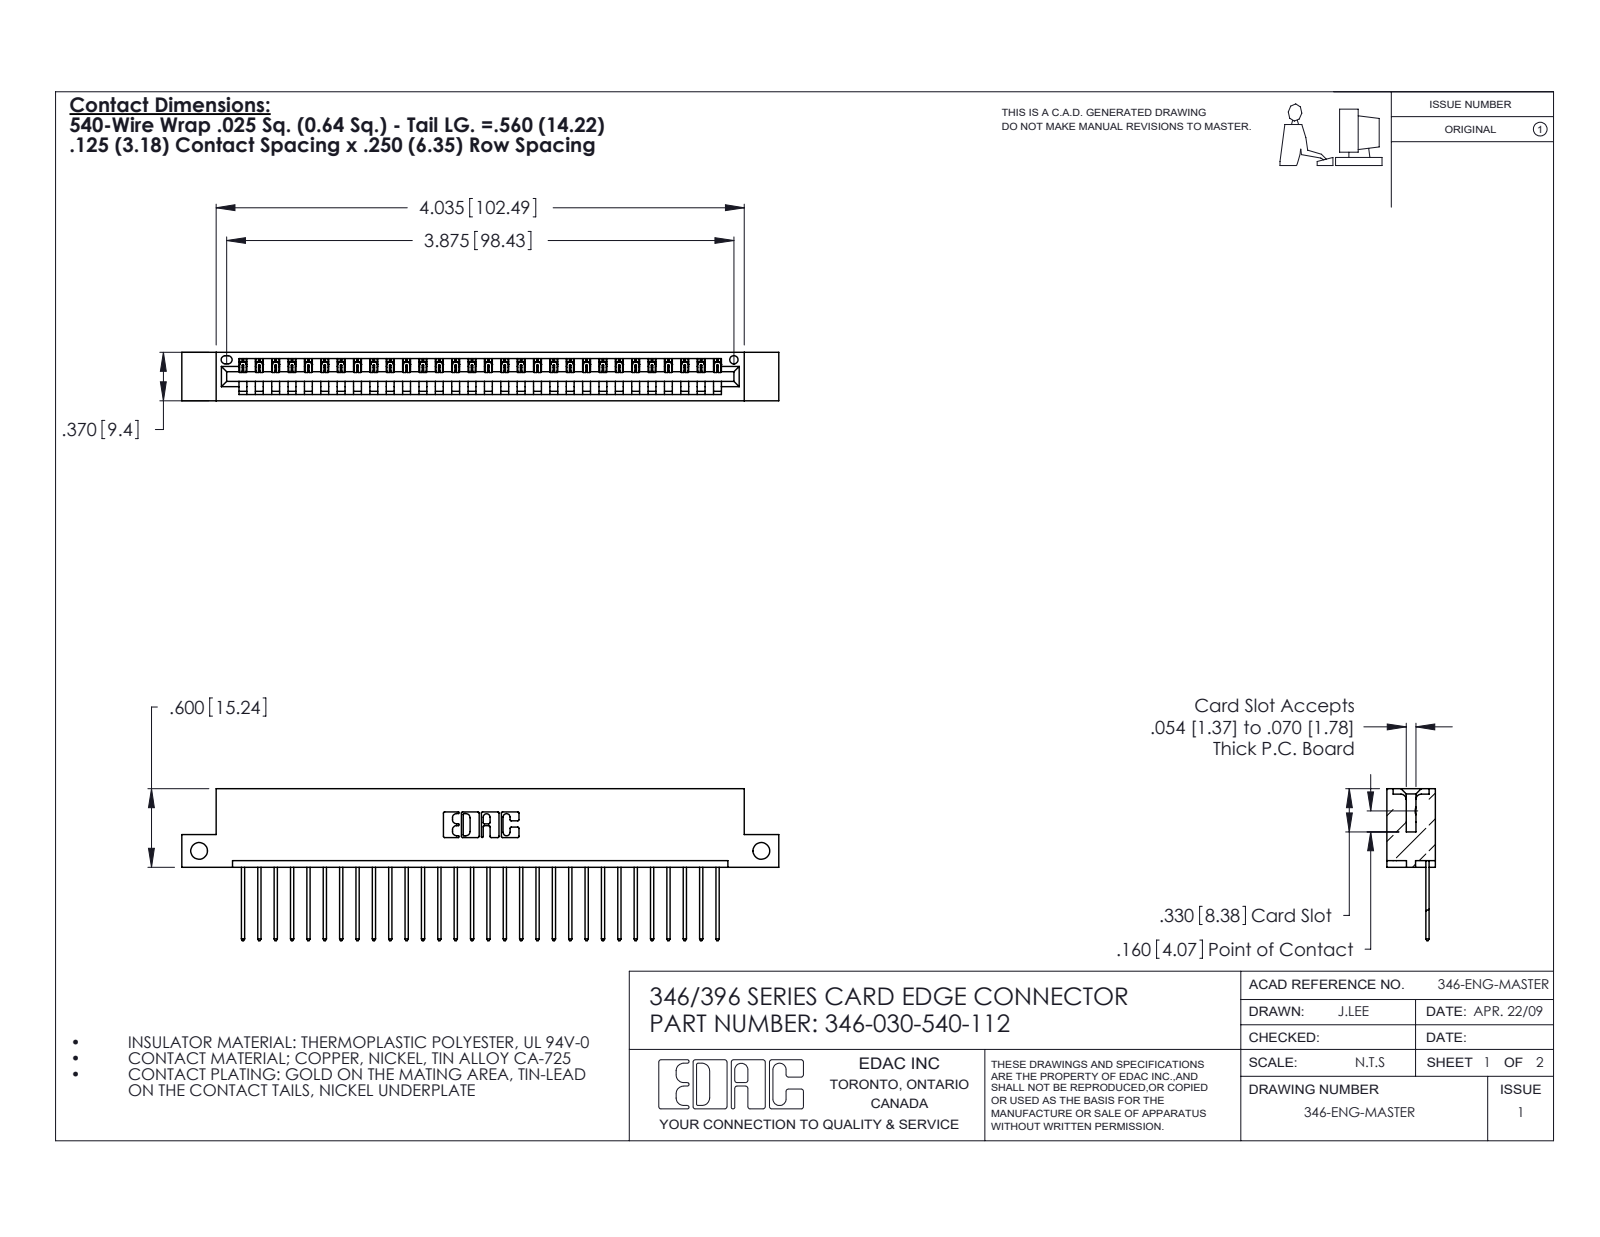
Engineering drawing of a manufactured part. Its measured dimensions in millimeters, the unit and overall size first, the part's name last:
Units: millimetres
Overall size (bounding box): 115.8 × 29.5 × 9.4
Round holes (diameter × count): ⌀3.3 ×2, ⌀1.6 ×1
Partial cylindrical surfaces — rounded edges, fillets, slot ends (radius × count): R0.2 ×60, R0.3 ×60, R0.3 ×22, R0.2 ×6, R0.8 ×6, R0.7 ×3, R0.8 ×2, R1 ×2
Main face-to-face distances: 1.2, 8.2, 6.4, 9.4, 1.8, 7.6, 0.6, 3.8, 5.6, 2.5
Hole centre spacings: 109.1
Volume: 11 000 mm³ · Surface area: 13 720 mm²
Bodies: 31 solids, 1862 faces (1276 planar, 586 cylindrical, 0 other)
Part name (STEP PRODUCT): 346 Part_Flush Mounting Lugs - Side Mount; 345-292-001_345-293-140; 346-030-540-112
STEP written by: SolidWorks 2020 (CONFIG_CONTROL_DESIGN)
